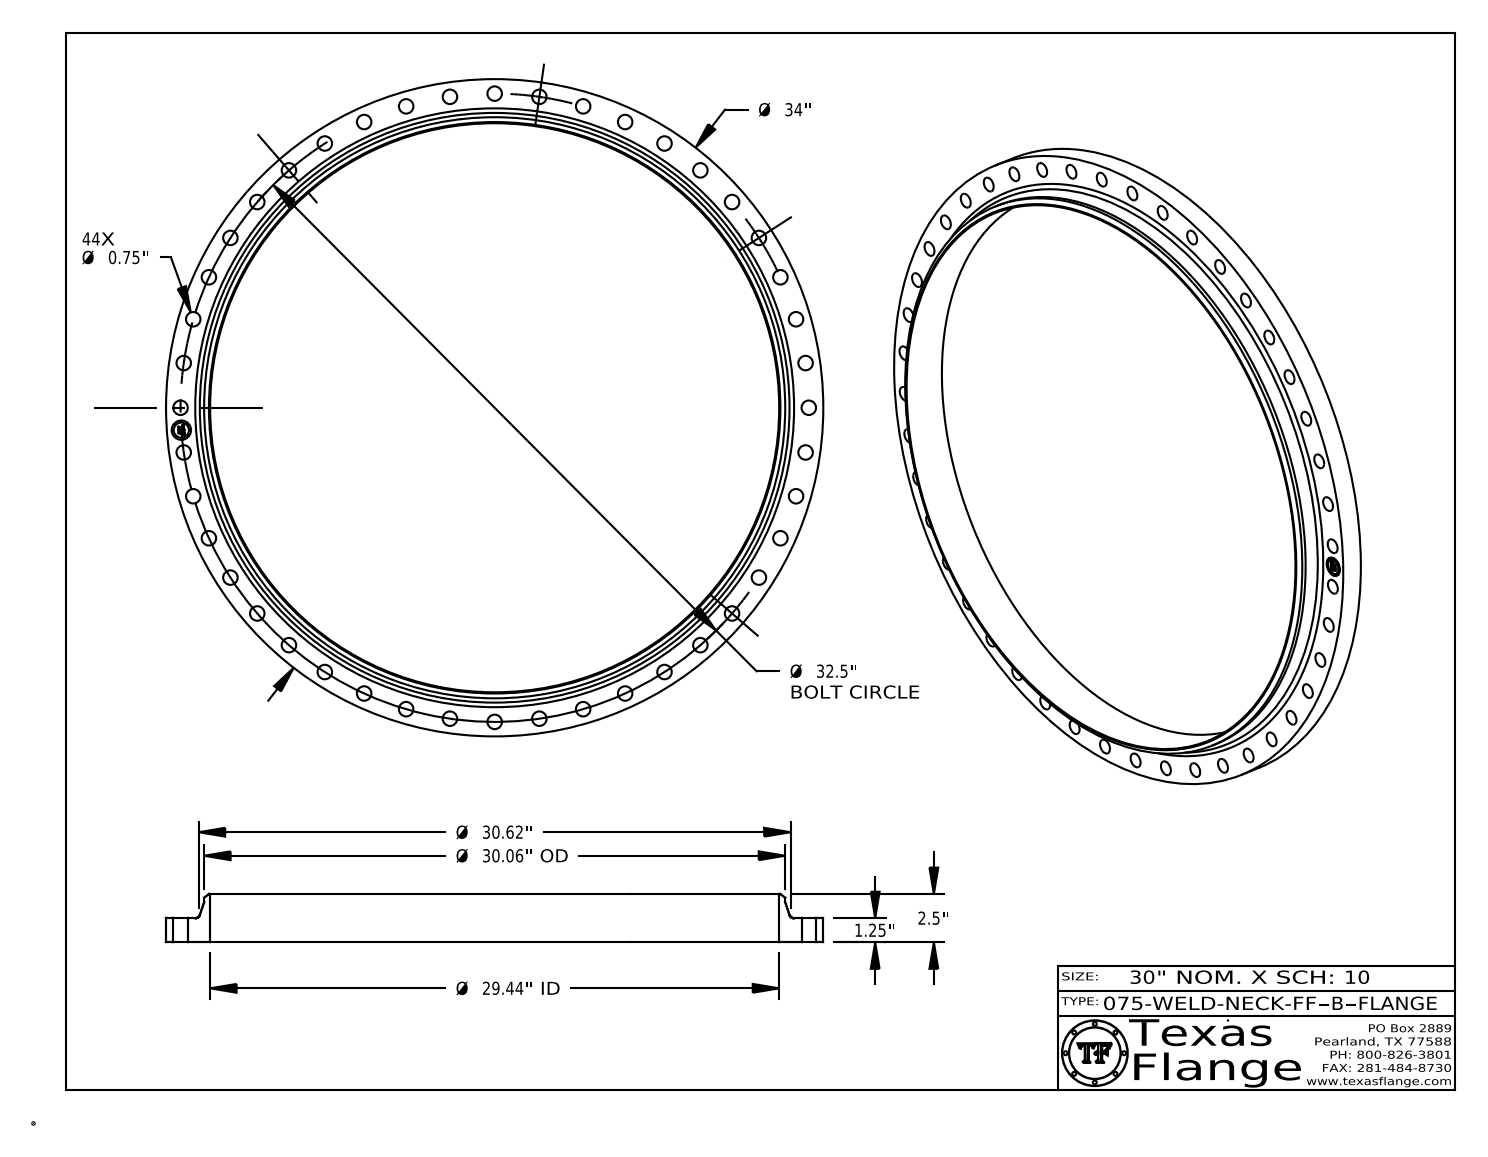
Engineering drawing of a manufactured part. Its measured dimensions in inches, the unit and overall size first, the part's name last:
Units: inches
Overall size (bounding box): 34 × 34 × 2.5
Round holes (diameter × count): ⌀0.75 ×44, ⌀1 ×1, ⌀29.436 ×1
Round bosses / shafts (diameter × count): ⌀0.061 ×8, ⌀34 ×1, ⌀30.06 ×1, ⌀0.788 ×1
Main face-to-face distances: 1.25, 2.5, 1.235, 0.015, 1.265, 0.298, 0.292, 0.054, 0.193, 0.248
Hole centre spacings: 16.25, 32.417, 32.169, 31.183, 9.156, 4.625, 29.563, 31.757
Volume: 305.6 in³ · Surface area: 990.4 in²
Bodies: 1 solid, 488 faces (368 planar, 114 cylindrical, 6 other)
Part name (STEP PRODUCT): 075-WELD-NECK-FF, Series B
STEP written by: CATIA V5 STEP AP214 (AUTOMOTIVE_DESIGN)
